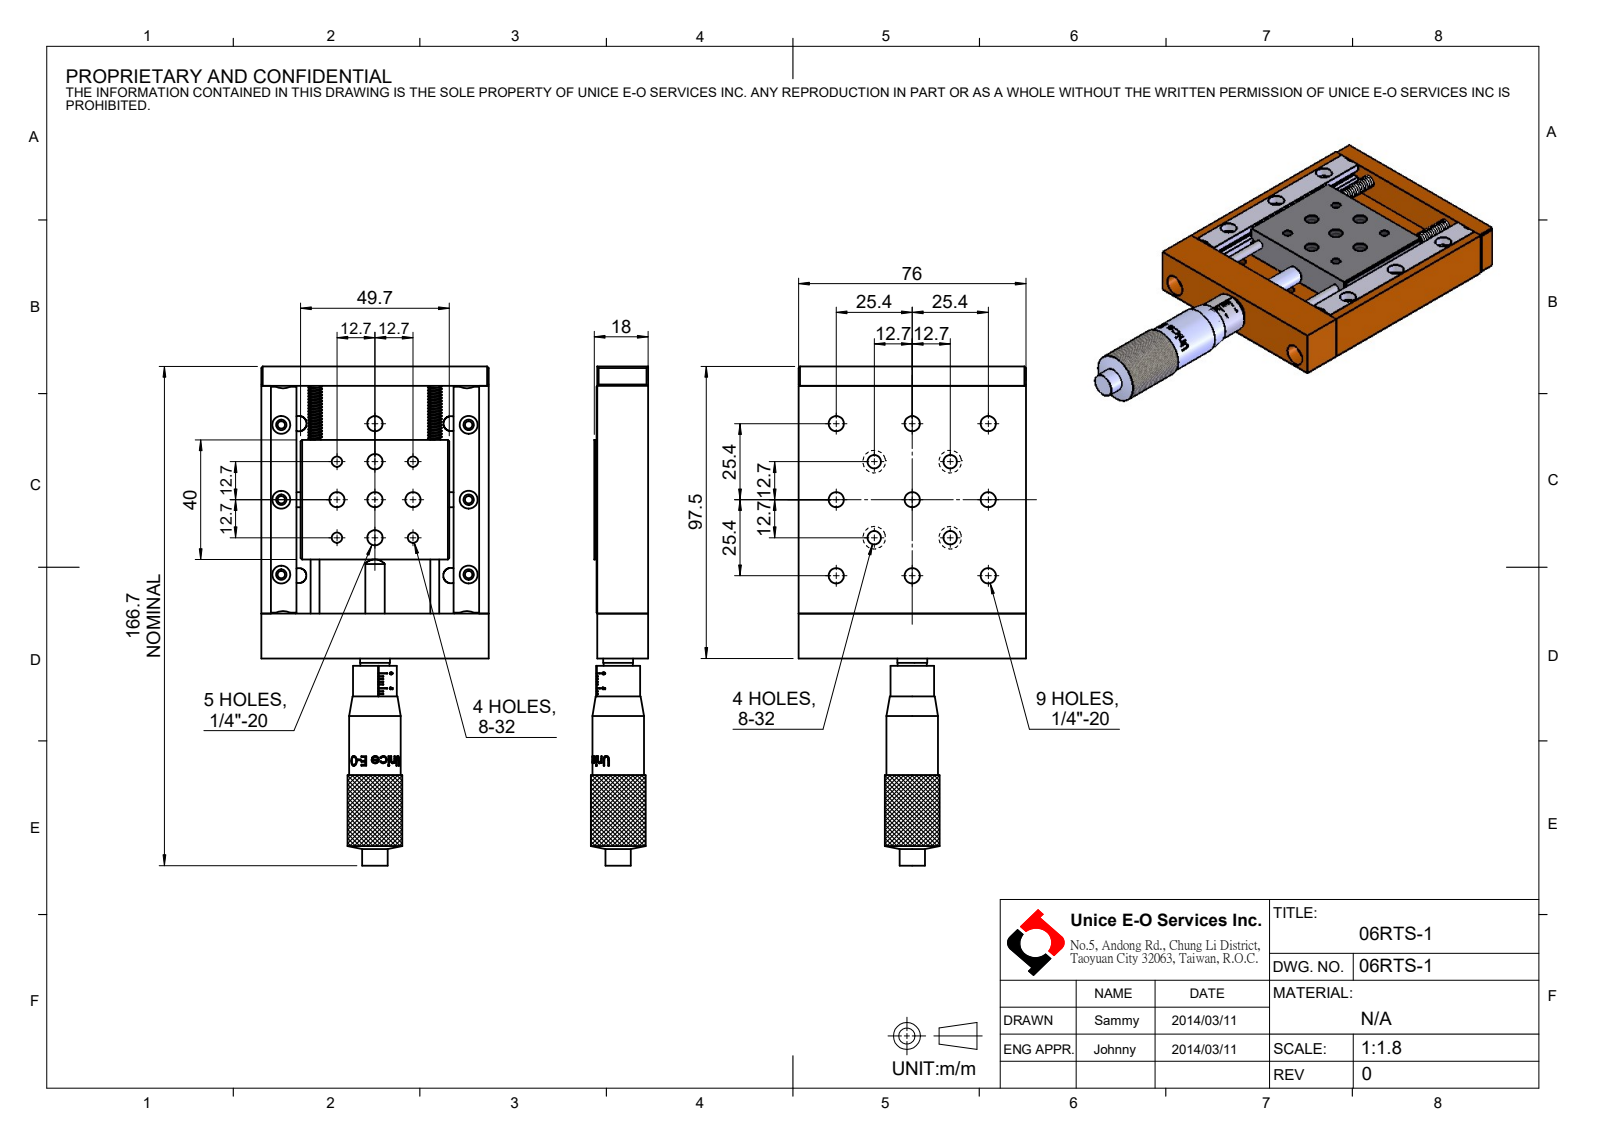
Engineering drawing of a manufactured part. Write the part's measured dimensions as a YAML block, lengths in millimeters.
part_name: "06RTS-1"
step_written_by: "SolidWorks 2016 (CONFIG_CONTROL_DESIGN)"
units: millimeters
bodies: {solids: 12, faces: 758, planar: 405, cylindrical: 187, other: 166}
overall_size: [166.7, 76, 19.15]
volume: 108098
surface_area: 55853
round_holes:
  - {diameter: 5.11, count: 13}
  - {diameter: 2.5, count: 7}
  - {diameter: 3.5, count: 6}
  - {diameter: 6, count: 6}
  - {diameter: 3.3, count: 4}
  - {diameter: 3.45, count: 4}
  - {diameter: 4.5, count: 4}
  - {diameter: 4.5, count: 4}
  - {diameter: 7.54, count: 4}
  - {diameter: 3, count: 3}
  - {diameter: 3.1, count: 2}
  - {diameter: 3.2, count: 2}
round_bosses_or_shafts:
  - {diameter: 3, count: 2}
  - {diameter: 18.3, count: 1}
  - {diameter: 17.2, count: 1}
  - {diameter: 14.6, count: 1}
  - {diameter: 9.75, count: 1}
  - {diameter: 8.5, count: 1}
  - {diameter: 6.5, count: 1}
partial_cylinders:
  - {radius: 8.55, count: 1}
face_to_face_distances: [9, 12, 5, 1, 76, 18, 4, 3.2, 72.8, 8]
hole_center_spacings: [28.4, 17.96, 25.4, 12.7, 40.16, 35.92, 45.79, 56.8]
